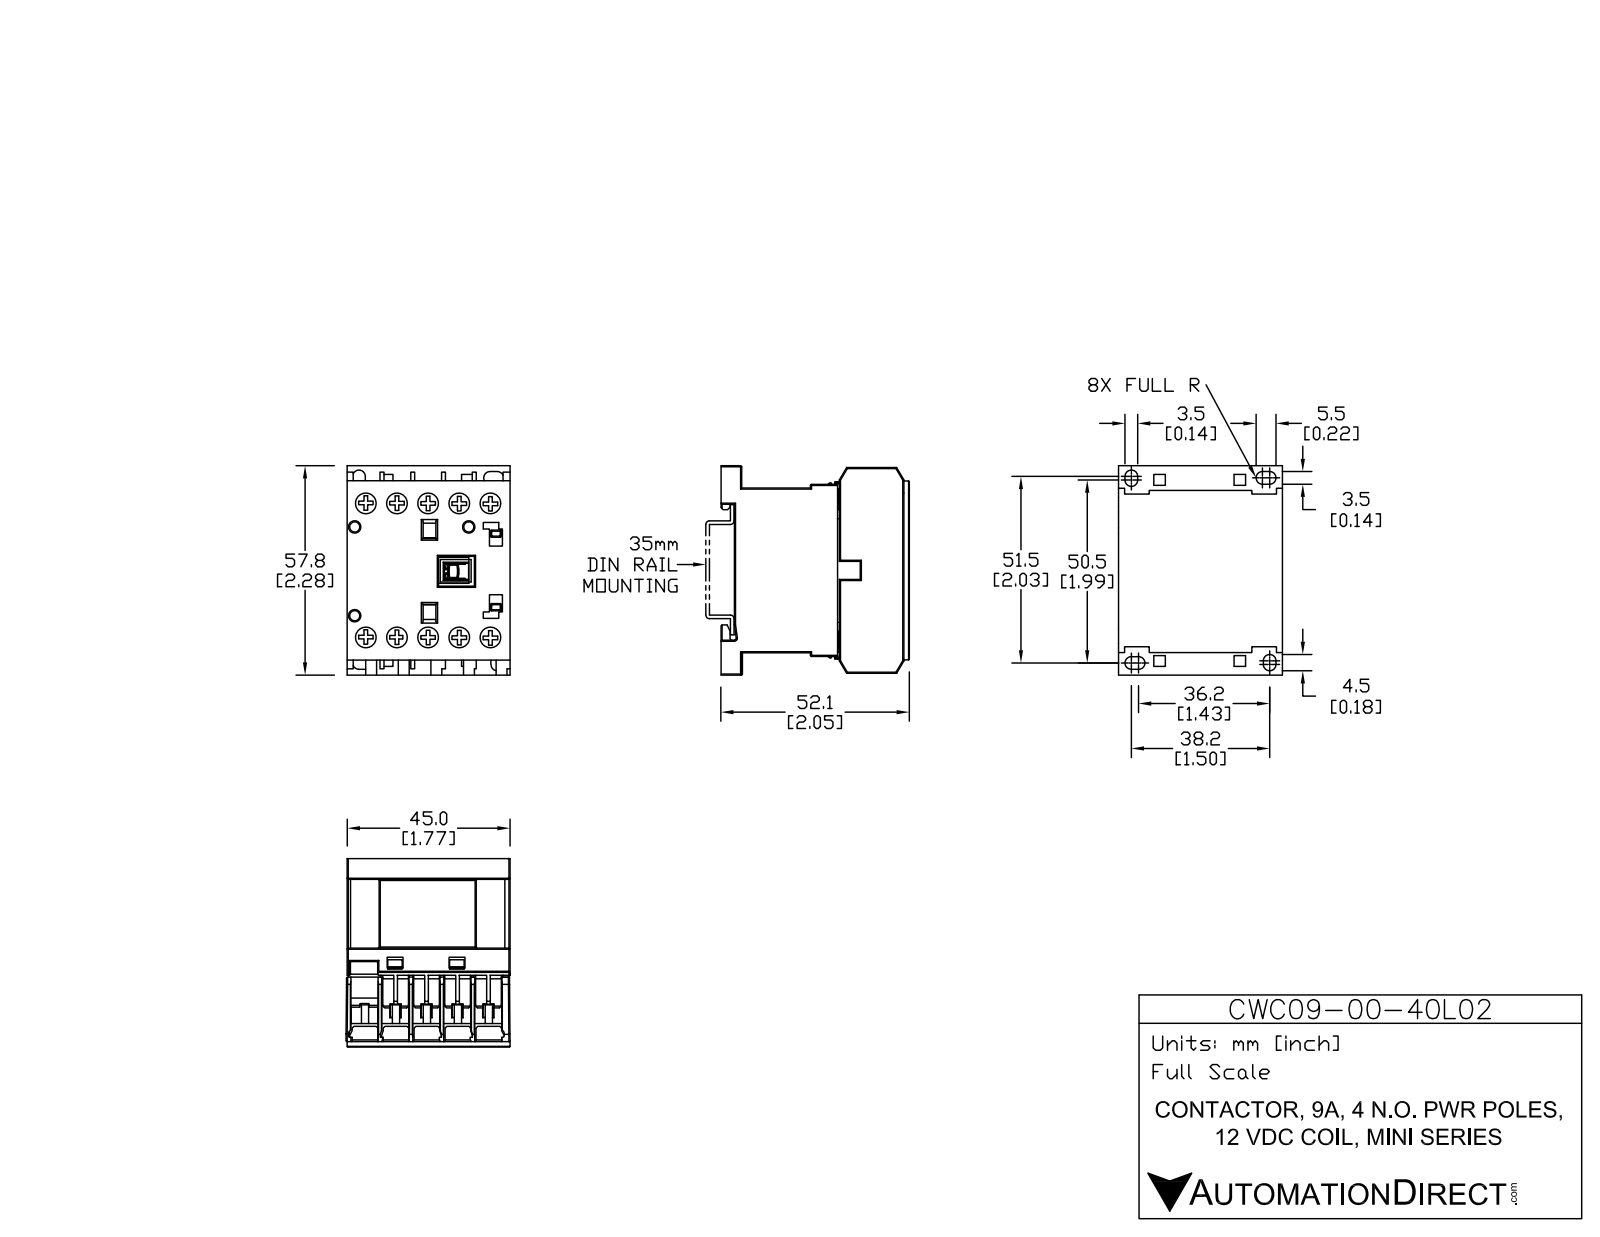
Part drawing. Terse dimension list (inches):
name: CWC09-00-40L02
written by: SolidWorks 2013 (AUTOMOTIVE_DESIGN)
unit: in
bodies: 15 solids, 535 faces (445 planar, 90 cylindrical, 0 other)
size: 2.285 × 2.052 × 1.801
volume: 5.927 in³; area: 47.18 in²
holes: 10× ⌀0.244, 3× ⌀0.11
bosses: 10× ⌀0.232
rounds: 20× R0.012, 6× R0.068, 2× R0.068, 1× R0.013, 1× R0.017, 1× R0.022
face distances: 0.325, 1.791, 0.049, 0.65, 0.374, 0.217, 0.699, 0.202, 0.419, 0.276
hole spacings: 0.337, 1.494, 0.673, 1.603, 1.455, 1.01, 1.771, 0.272
